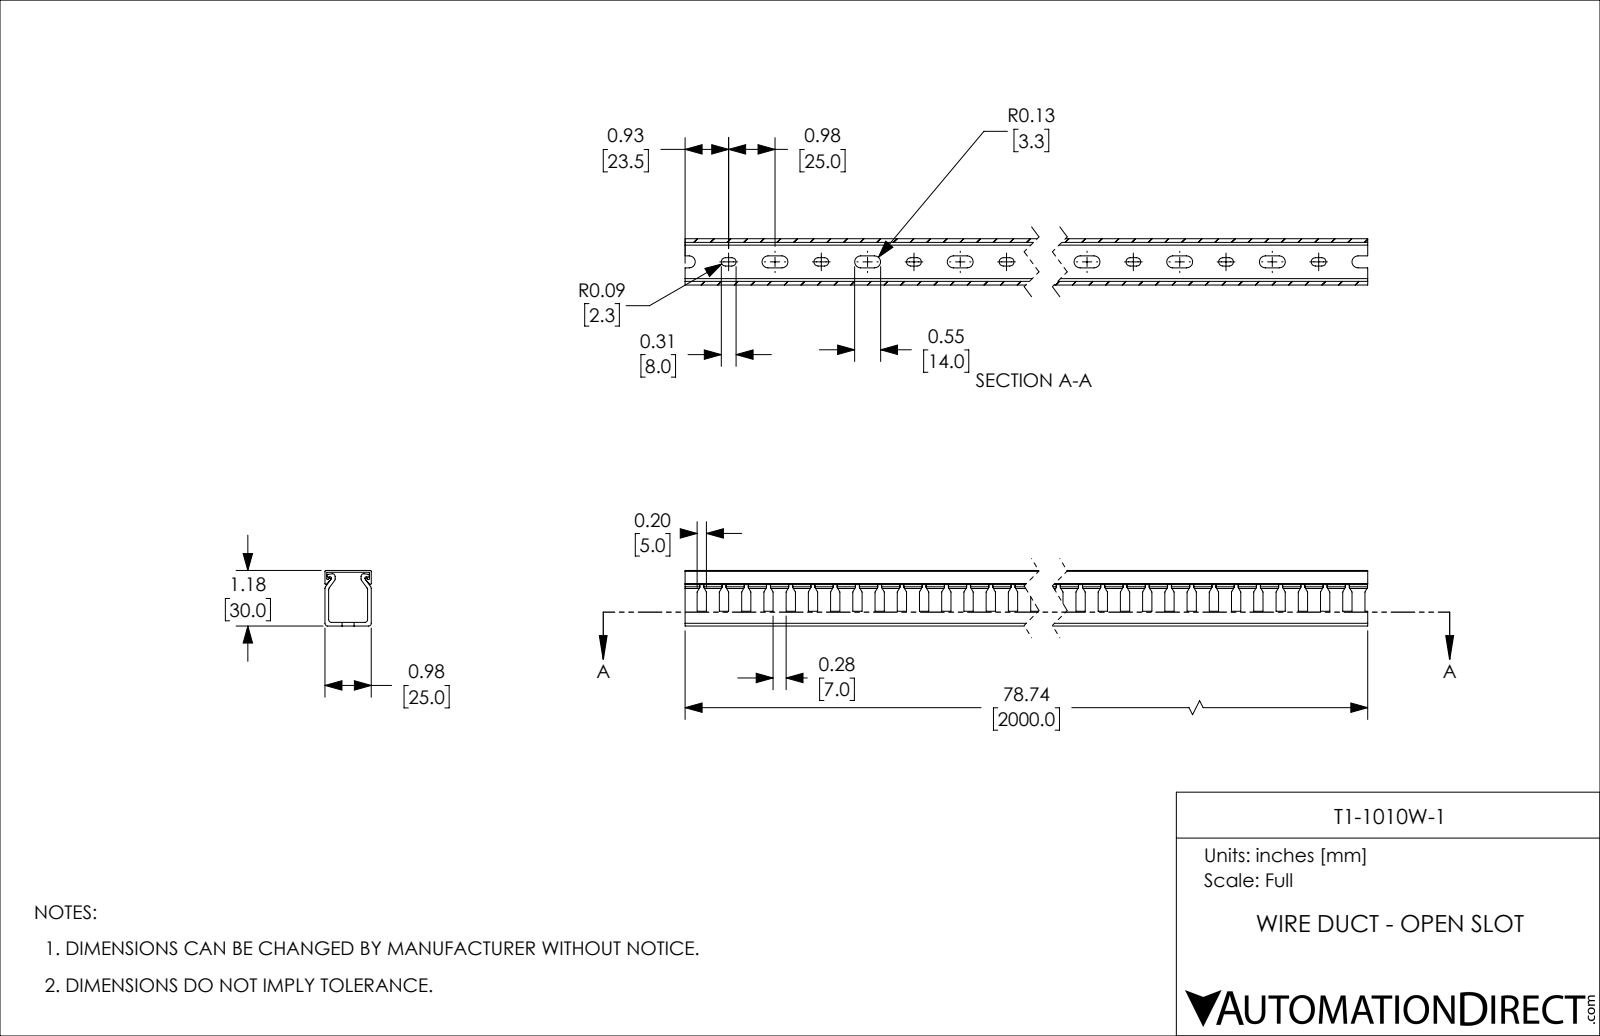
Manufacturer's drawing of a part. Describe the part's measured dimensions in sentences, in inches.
The part is named "T1-1010W-1". Its 3-D file was written by "SolidWorks 2021 (CONFIG_CONTROL_DESIGN)". It is 2 solids with 945 faces: 514 planar, 431 cylindrical and 0 other. Overall it measures 78.74 by 1.181 by 0.984 inches. Its volume is 24.87 cubic inches and its surface area 770 square inches. Partial cylindrical surfaces (rounded edges, fillets, slot ends): 80 of radius 0.089, 80 of radius 0.128, 12 of radius 0.059, 8 of radius 0.02, 6 of radius 0.03. The main face-to-face distances are 0.079, 0.039, 0.906, 0.984, 1.142, 1.181, 0.827, 1.063, 1.102, 0.945.
